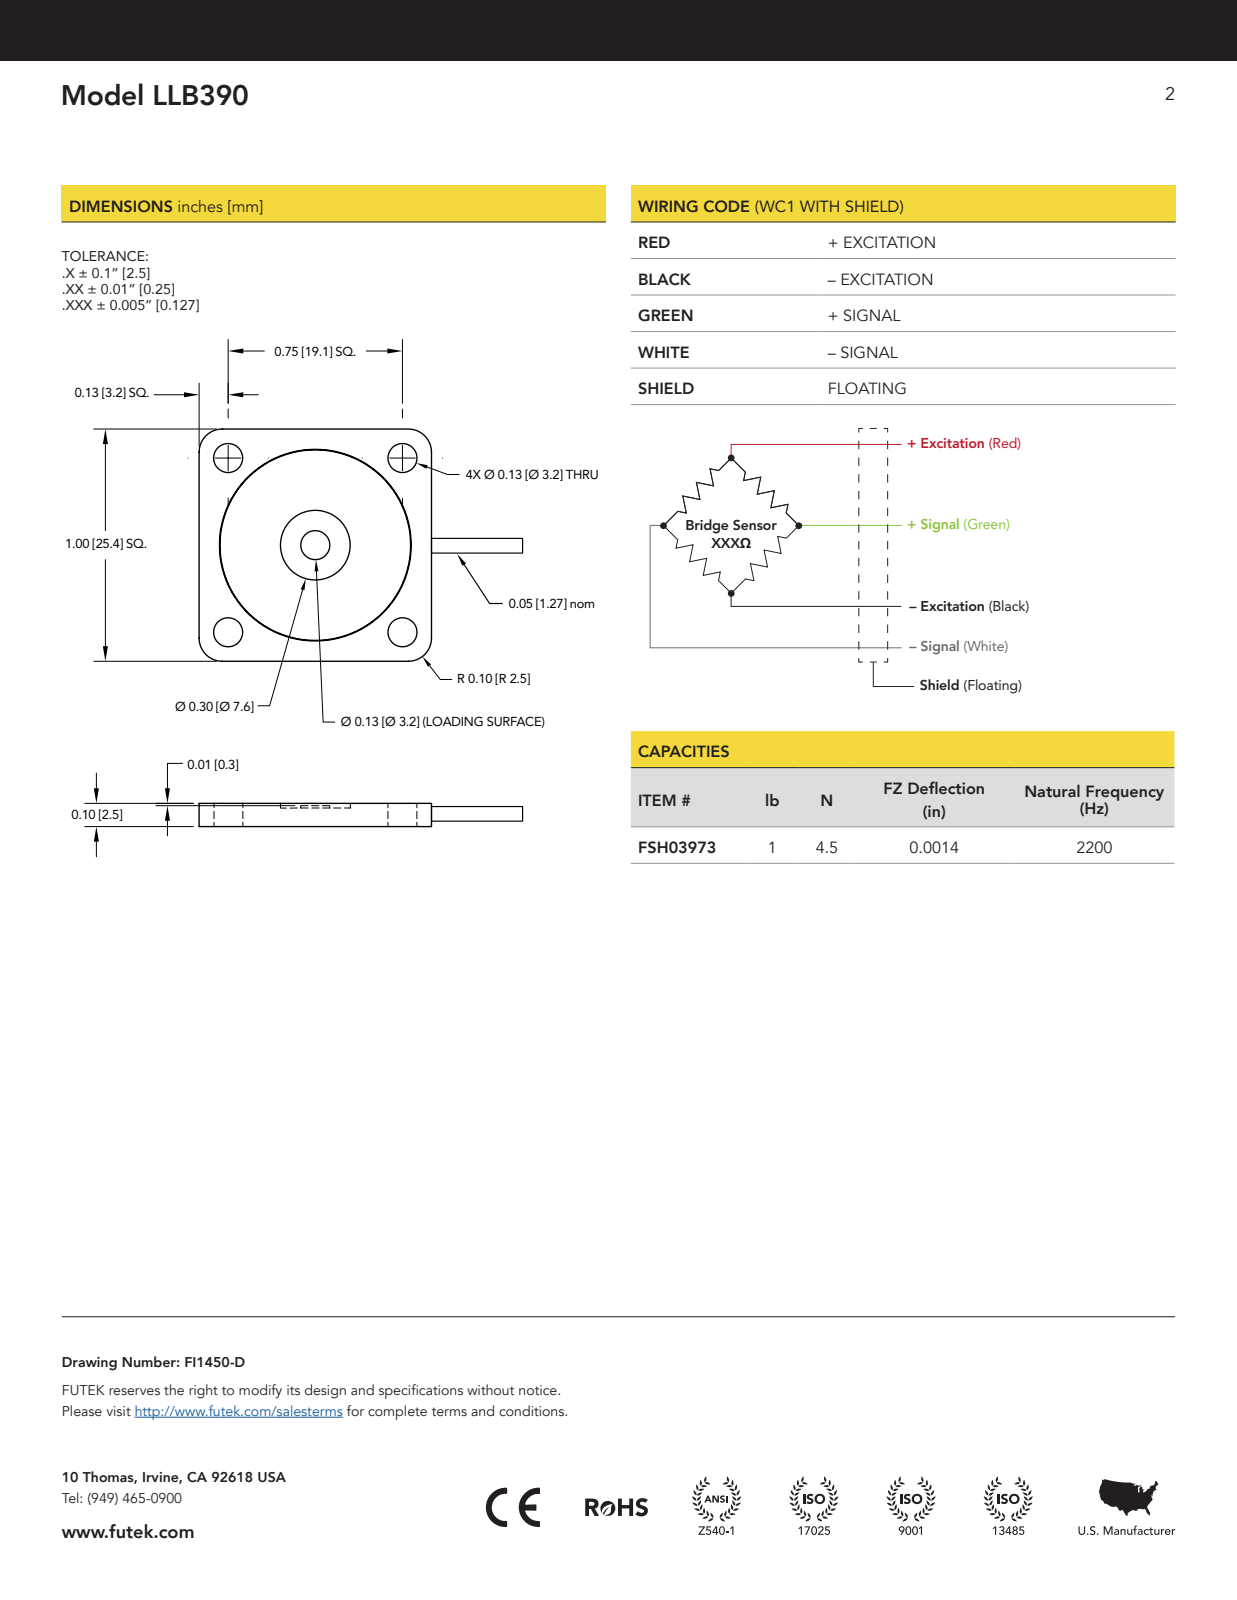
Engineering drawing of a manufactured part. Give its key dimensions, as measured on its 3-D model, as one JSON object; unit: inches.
{"part_name": "LLB390; COVER; 59E7; 59E7A", "step_written_by": "Autodesk Inventor 2008 (AUTOMOTIVE_DESIGN)", "units": "inches", "bodies": {"solids": 2, "faces": 34, "planar": 16, "cylindrical": 16, "other": 2}, "overall_size": [2.404, 1, 0.1], "volume_in3": 0.072, "surface_area_in2": 4.583, "round_holes": [[0.125, 4], [0.052, 1], [0.3, 1], [0.75, 1], [0.78, 1], [0.825, 1]], "round_bosses_or_shafts": [[0.82, 1], [0.125, 1]], "partial_cylinders_radius": [[0.1, 4]], "face_to_face_distances": [0.082, 0.097, 0.085, 0.015, 0.052, 0.04, 0.094, 0.042, 0.077, 0.065], "hole_center_spacings": [0.75, 0.53, 1.061, 0.53, 0.531]}
